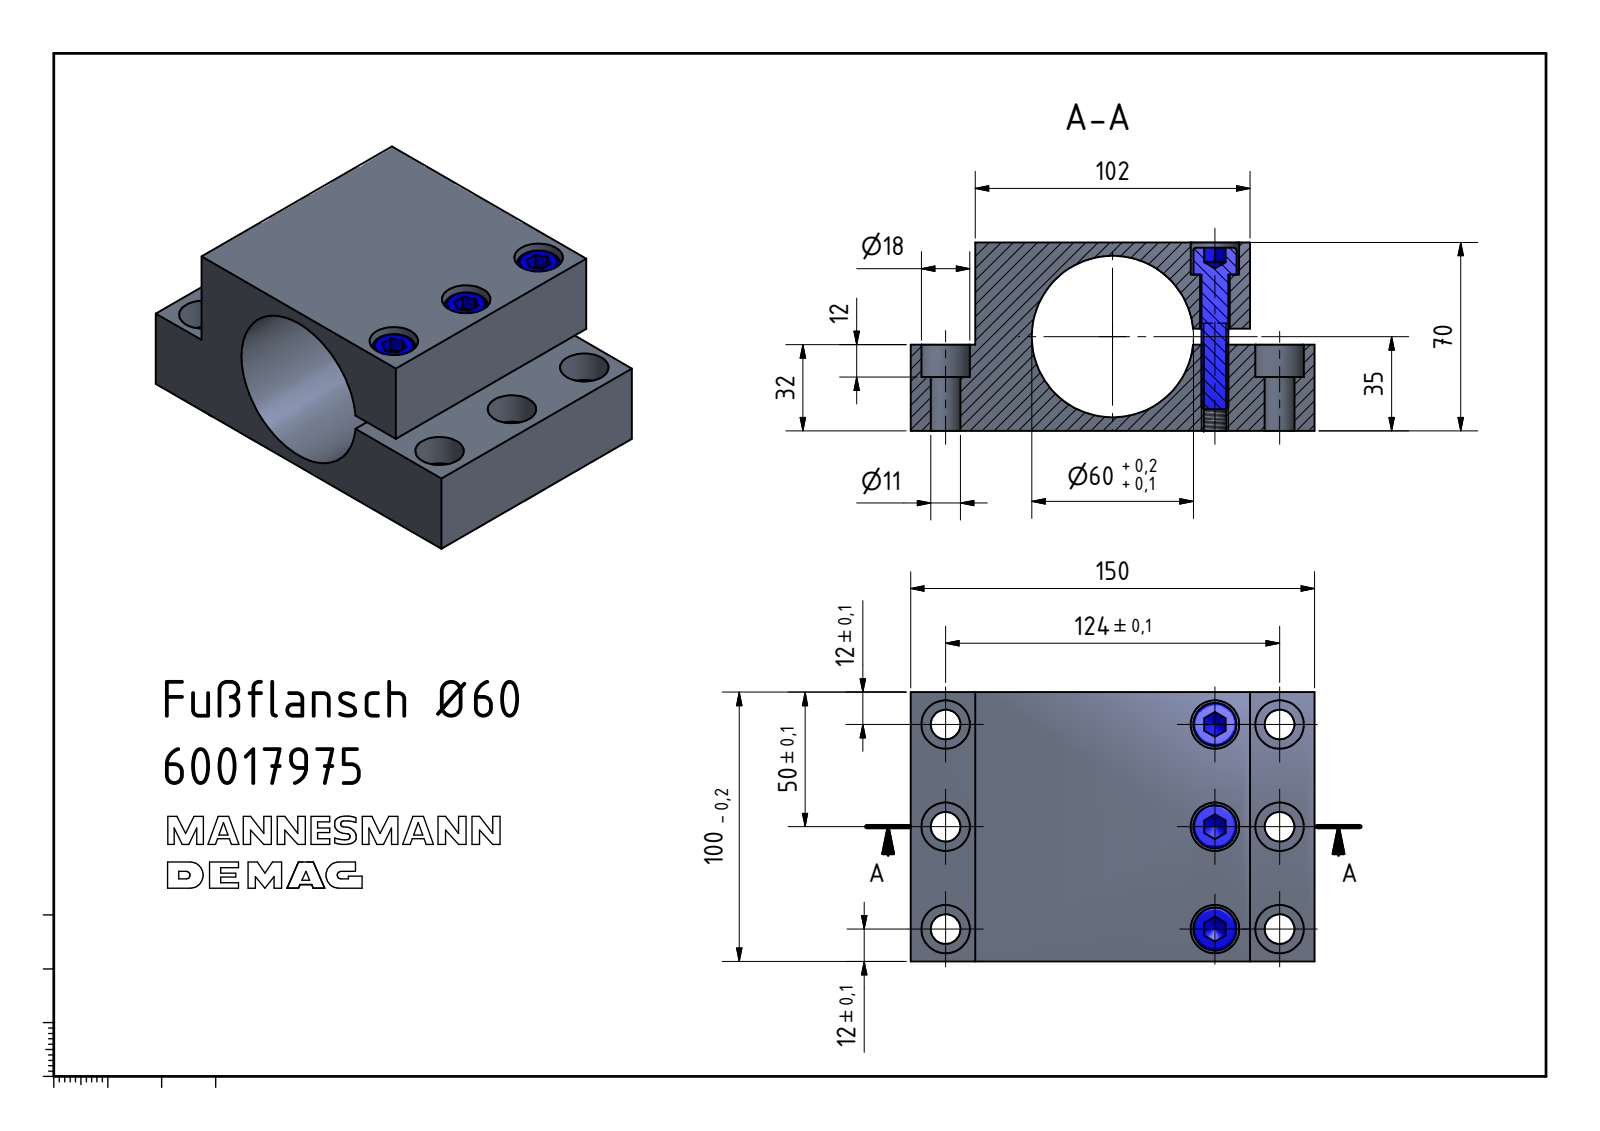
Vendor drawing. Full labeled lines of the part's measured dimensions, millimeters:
Part name (STEP PRODUCT): 60017975 Ø60 Fußflansch
STEP written by: Autodesk Inventor 2024 (AUTOMOTIVE_DESIGN)
Units: millimetres
Bodies: 1 solid, 128 faces (59 planar, 31 cylindrical, 38 other)
Overall size (bounding box): 150 × 97 × 70
Volume: 524 512 mm³ · Surface area: 86 710 mm²
Round holes (diameter × count): ⌀18 ×9, ⌀11 ×7, ⌀60 ×1
Round bosses / shafts (diameter × count): ⌀16 ×3, ⌀11 ×2, ⌀10 ×1
Partial cylindrical surfaces — rounded edges, fillets, slot ends (radius × count): R5 ×8
Main face-to-face distances: 70, 37.5, 32.5, 24, 126, 97, 150, 102, 5, 20.5
Hole centre spacings: 38, 44.94, 106.98, 129.69, 24, 76, 100, 124
